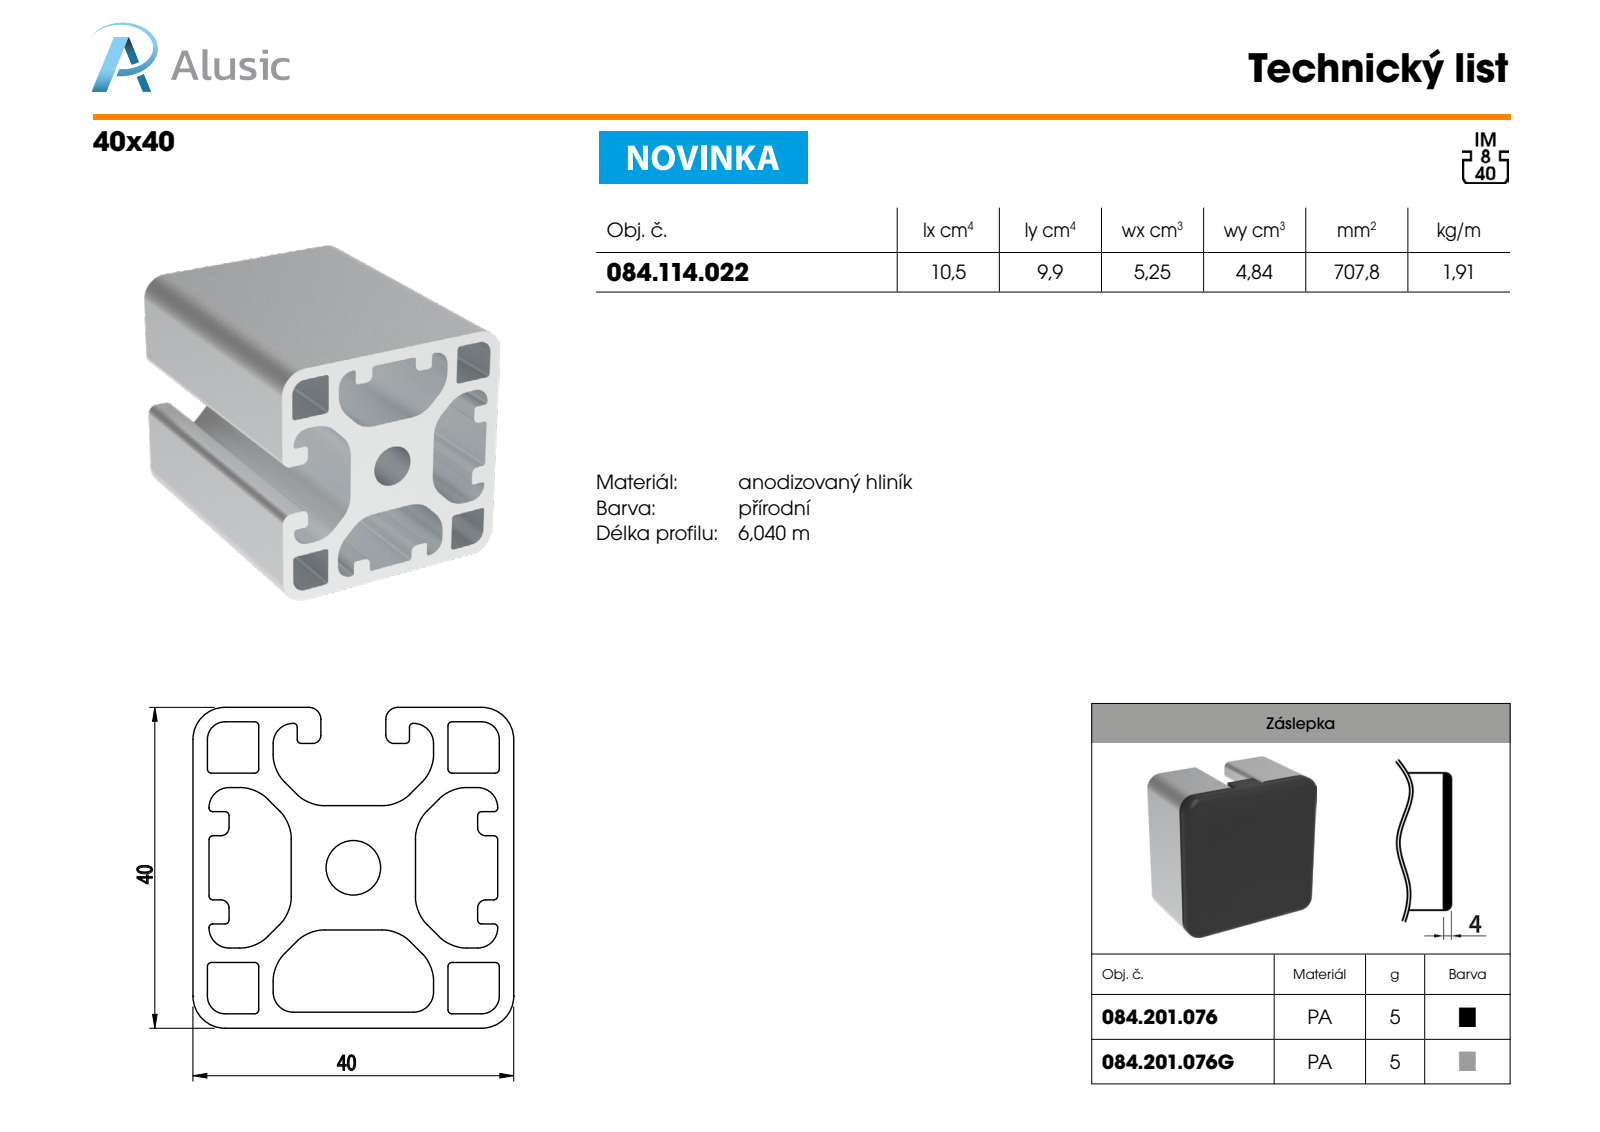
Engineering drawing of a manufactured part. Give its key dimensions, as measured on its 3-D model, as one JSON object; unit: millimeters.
{"part_name": "084.114.022", "step_written_by": "SolidWorks 2018 (AUTOMOTIVE_DESIGN)", "units": "millimeters", "bodies": {"solids": 1, "faces": 156, "planar": 78, "cylindrical": 78, "other": 0}, "overall_size": [100, 40, 40], "volume_mm3": 70780, "surface_area_mm2": 51271, "round_holes": [[6.8, 1]], "partial_cylinders_radius": [[0.5, 26], [5, 16], [0.45, 8], [1, 8], [2.5, 8], [2.2, 4], [4, 4], [1.5, 2]], "face_to_face_distances": [8.2, 40, 31.8, 1.8, 30, 19.55, 38.2, 6.4, 12.25, 27.75]}
